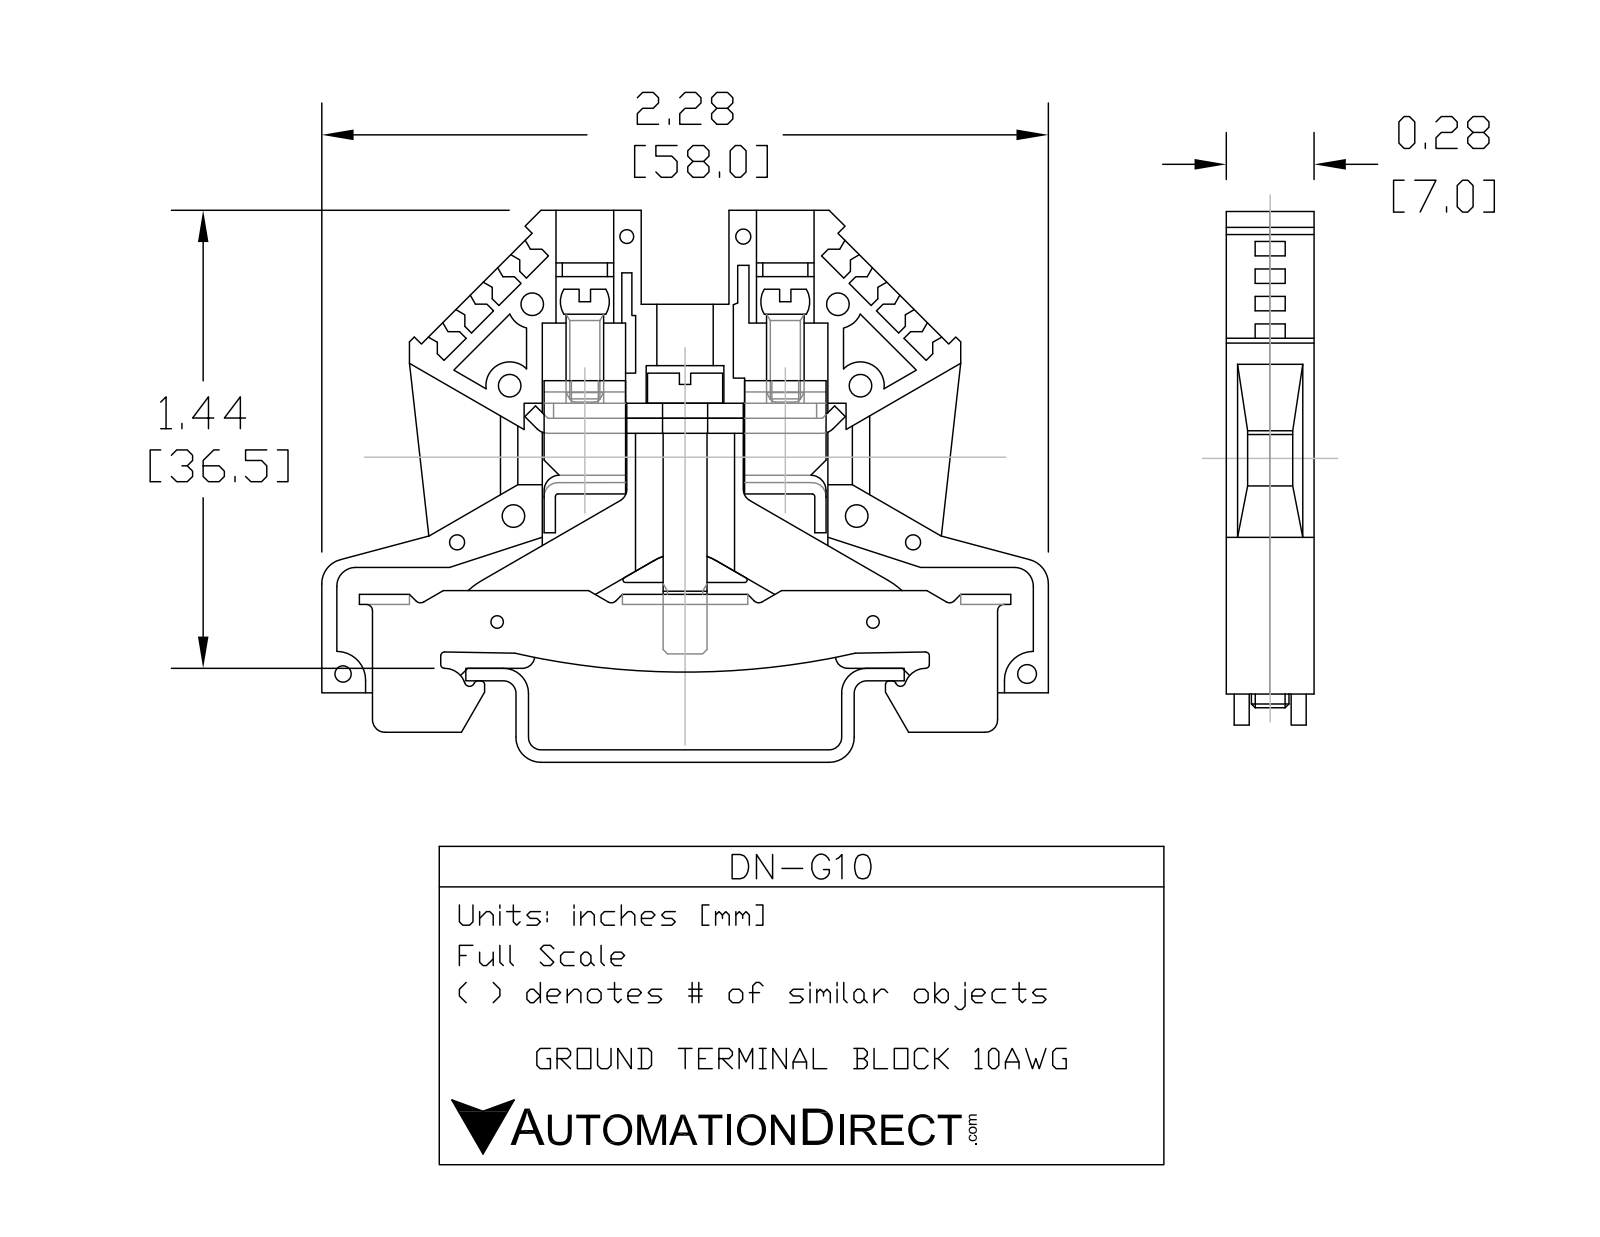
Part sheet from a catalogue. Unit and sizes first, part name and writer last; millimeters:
Units: millimetres
Overall size (bounding box): 58 × 40 × 7
Round holes (diameter × count): ⌀4.6 ×3
Round bosses / shafts (diameter × count): ⌀3.6 ×3
Partial cylindrical surfaces — rounded edges, fillets, slot ends (radius × count): R0.2 ×8, R0.3 ×4, R0.4 ×2, R1 ×2, R1.7 ×2, R2 ×2, R62 ×1
Main face-to-face distances: 7, 25.5, 32.5, 4, 0.62, 6.38, 34.5, 0.8, 38.5, 3
Hole centre spacings: 8, 16
Volume: 10 264 mm³ · Surface area: 5 139 mm²
Bodies: 1 solid, 214 faces (166 planar, 44 cylindrical, 4 other)
Part name (STEP PRODUCT): 20653; 43454_DN-G10
STEP written by: SolidWorks 2013 (AUTOMOTIVE_DESIGN)
